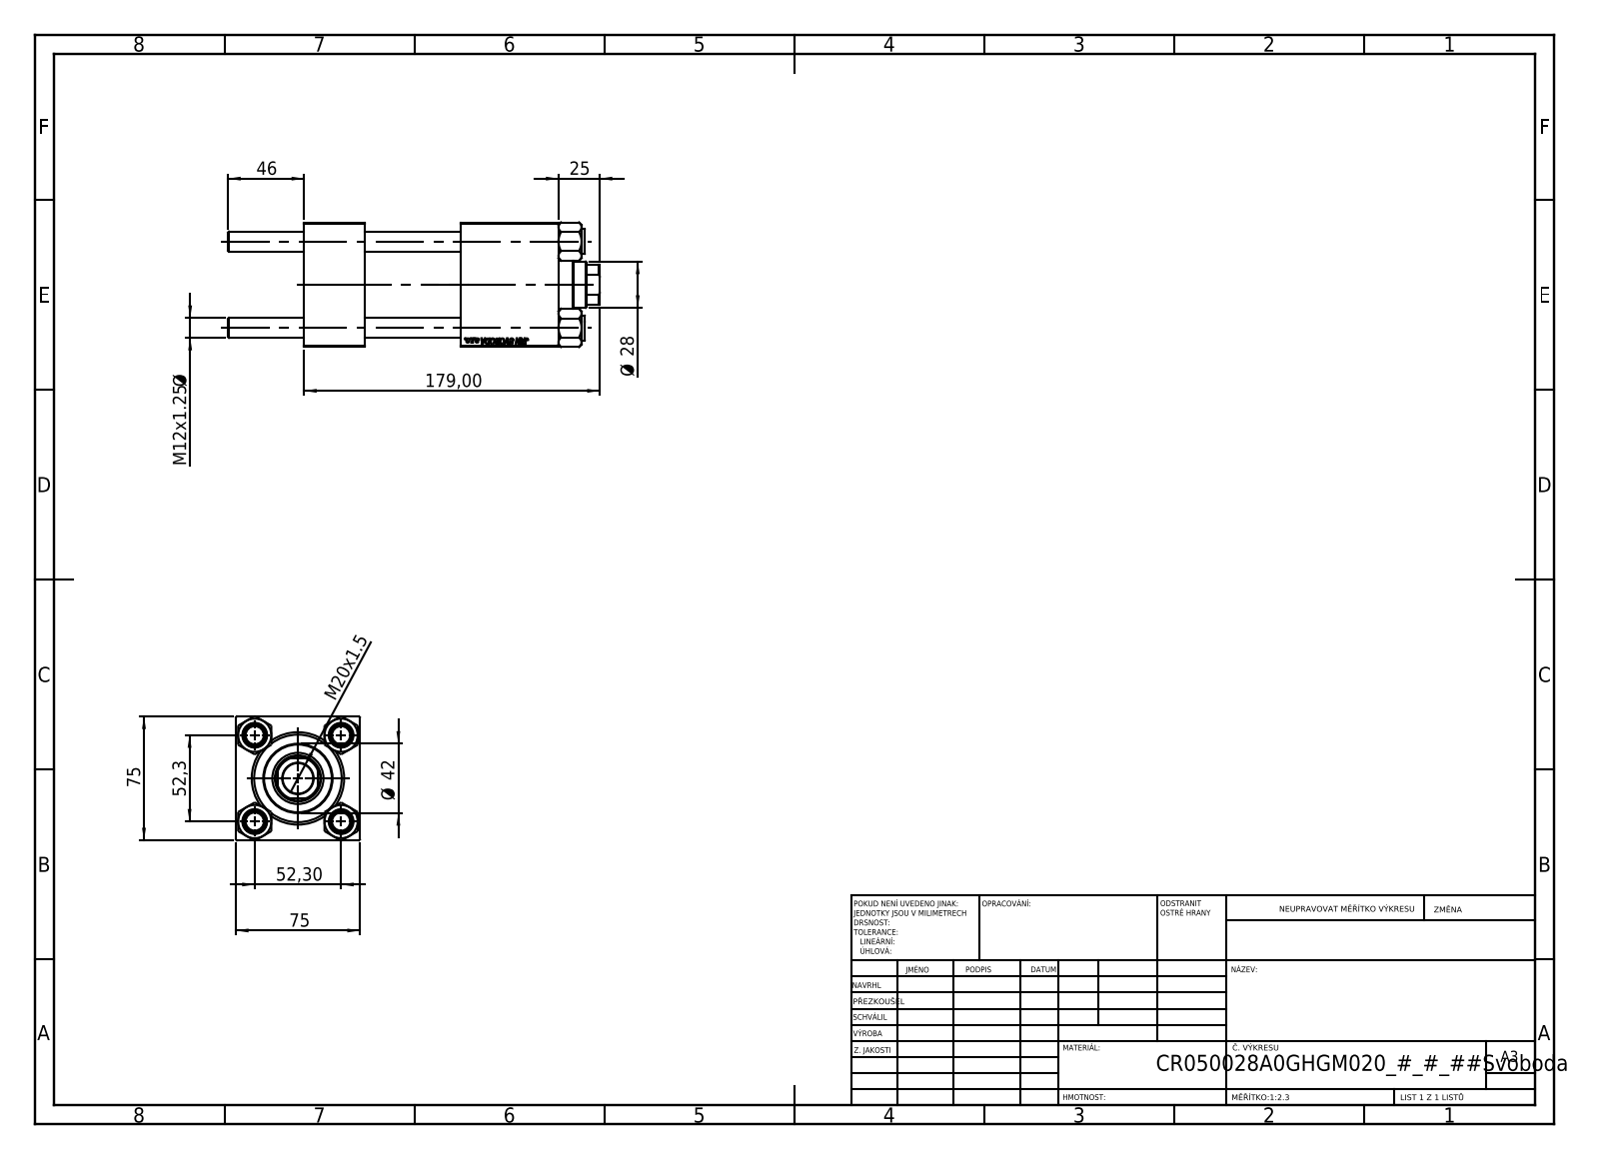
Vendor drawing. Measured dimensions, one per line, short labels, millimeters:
name: V215_VC_A; V215CR_VCP; CR025_012_A_0_G_A_G_M_020_+#_##_TYCINKA; V215CR_BODY_A (+1 more)
written by: SolidWorks 2019 (CONFIG_CONTROL_DESIGN)
unit: mm
bodies: 11 solids, 1134 faces (520 planar, 78 cylindrical, 536 other)
size: 225 × 75.54 × 75
volume: 702 211 mm³; area: 167 389 mm²
holes: 4× ⌀12, 2× ⌀7, 2× ⌀20.96, 2× ⌀30, 1× ⌀18.5, 1× ⌀28, 1× ⌀31, 1× ⌀41, 1× ⌀50, 1× ⌀53
bosses: 4× ⌀15, 1× ⌀56, 1× ⌀42
rounds: 1× R13.5
face distances: 75, 37, 154, 117, 95, 58, 59, 125.3, 88.3, 30.3
hole spacings: 36.98, 52.3, 73.96, 93.5
